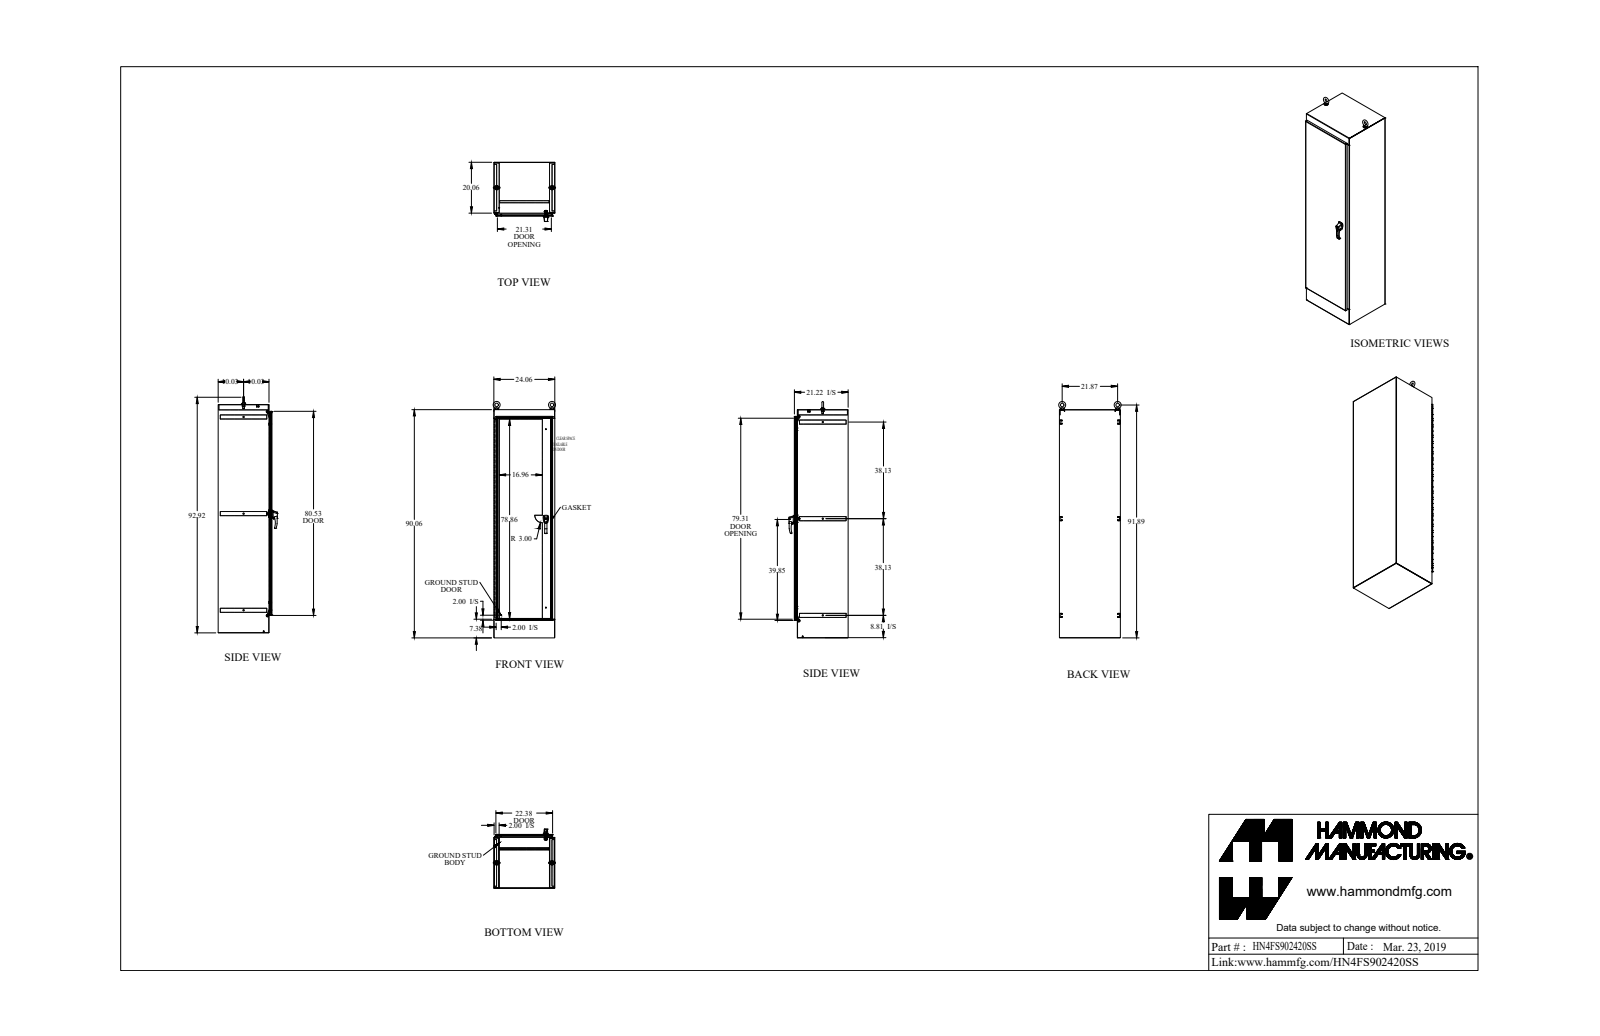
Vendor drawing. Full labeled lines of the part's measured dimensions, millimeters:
Part name (STEP PRODUCT): HN4FS902420SS
STEP written by: SolidWorks 2018 (AUTOMOTIVE_DESIGN)
Units: millimetres
Bodies: 53 solids, 2042 faces (932 planar, 945 cylindrical, 165 other)
Overall size (bounding box): 2374.6 × 624.9 × 593.4
Volume: 16 930 000 mm³ · Surface area: 14 030 000 mm²
Round holes (diameter × count): ⌀7.7 ×13, ⌀8.9 ×7, ⌀12.7 ×3, ⌀6.4 ×2, ⌀6.5 ×2, ⌀7.1 ×2, ⌀7.1 ×2, ⌀8 ×2, ⌀9.9 ×2, ⌀10.5 ×2, ⌀13.4 ×2, ⌀15.9 ×2
Round bosses / shafts (diameter × count): ⌀44.5 ×2, ⌀38.1 ×2, ⌀31.8 ×2, ⌀25.4 ×2, ⌀19.1 ×2, ⌀18.7 ×2, ⌀16 ×2, ⌀11.2 ×2
Partial cylindrical surfaces — rounded edges, fillets, slot ends (radius × count): R1.1 ×42, R3.5 ×36, R12.7 ×23, R3.2 ×22, R0.4 ×16, R1.2 ×15, R1.5 ×15, R3.6 ×15
Main face-to-face distances: 2.4, 537.3, 608.7, 606.3, 534.8, 611.1, 539.7, 2285.1, 507.1, 30.1
Hole centre spacings: 152.4, 304.8, 457.2, 609.6, 762, 914.4, 1066.8, 1219.2
